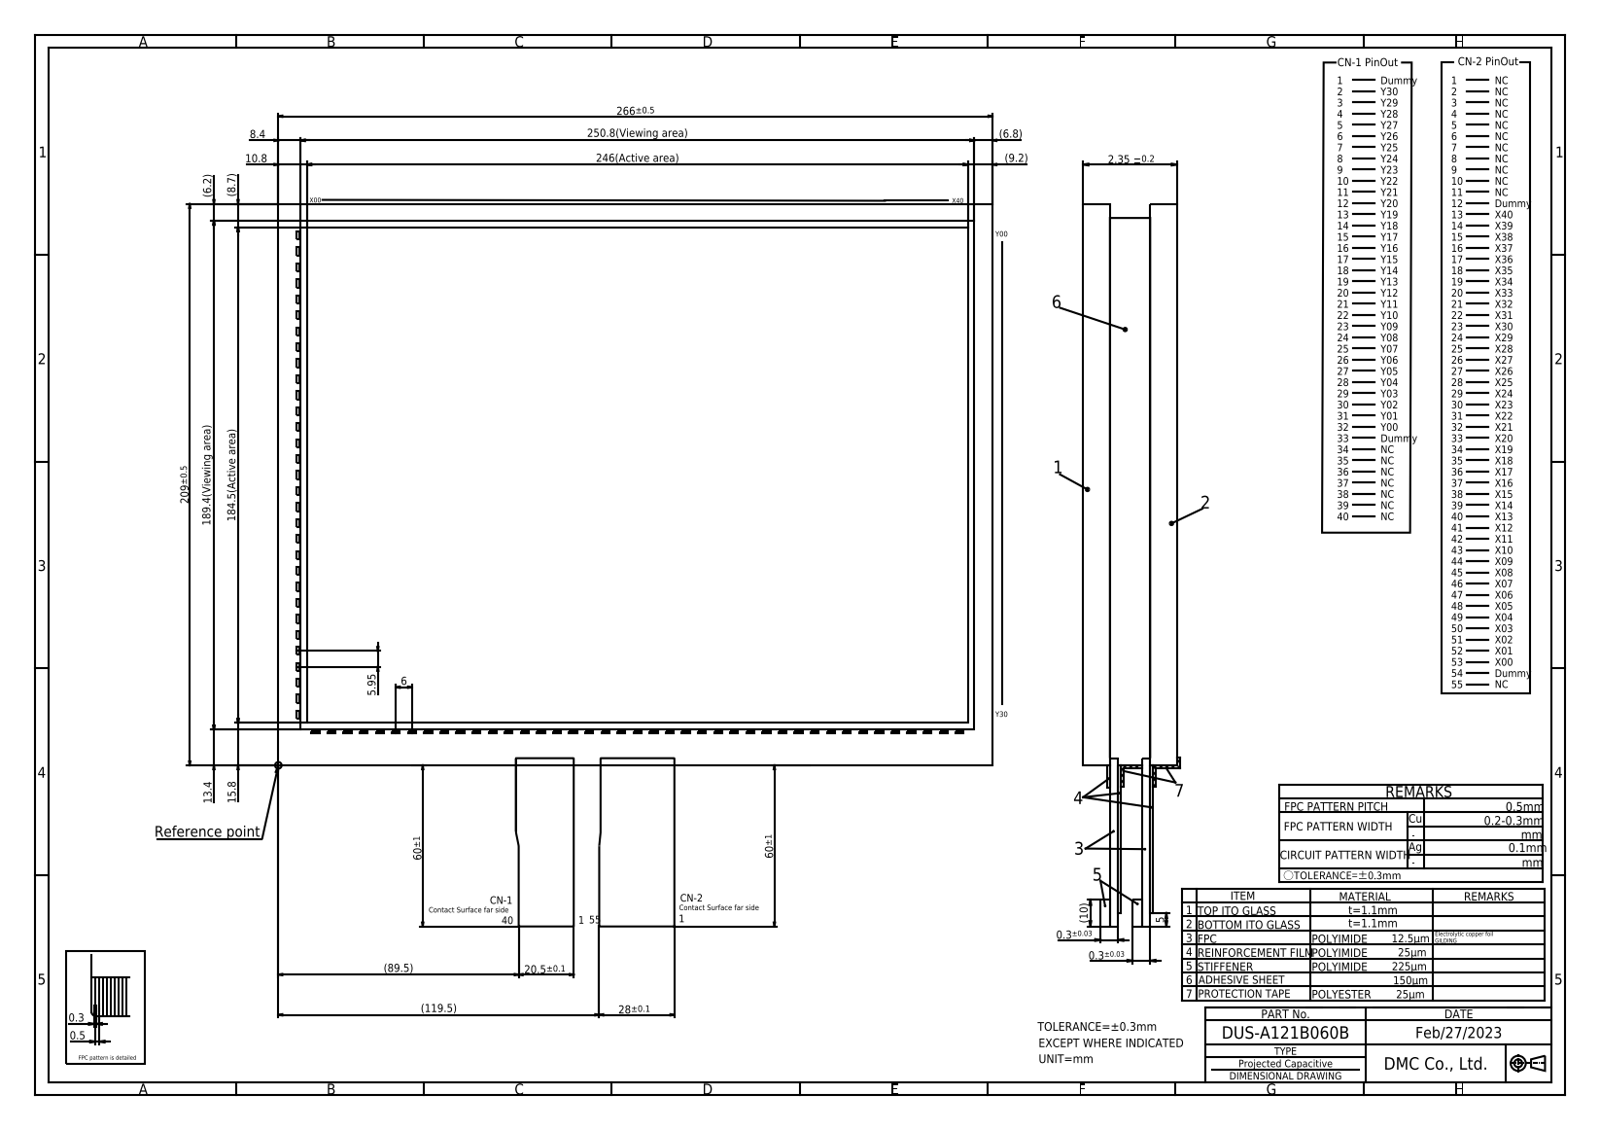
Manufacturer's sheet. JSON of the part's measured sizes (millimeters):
{"part_name": "DUS-A121B060B", "step_written_by": "Autodesk Inventor 2020 (CONFIG_CONTROL_DESIGN)", "units": "millimeters", "bodies": {"solids": 1, "faces": 422, "planar": 418, "cylindrical": 4, "other": 0}, "overall_size": [372.4, 310.8, 2.35], "volume_mm3": 130847, "surface_area_mm2": 119514, "partial_cylinders_radius": [[0.2, 4]], "face_to_face_distances": [2.35, 1.1, 1.15, 1.2, 1.25, 1, 2.25, 209, 266, 0.8]}
